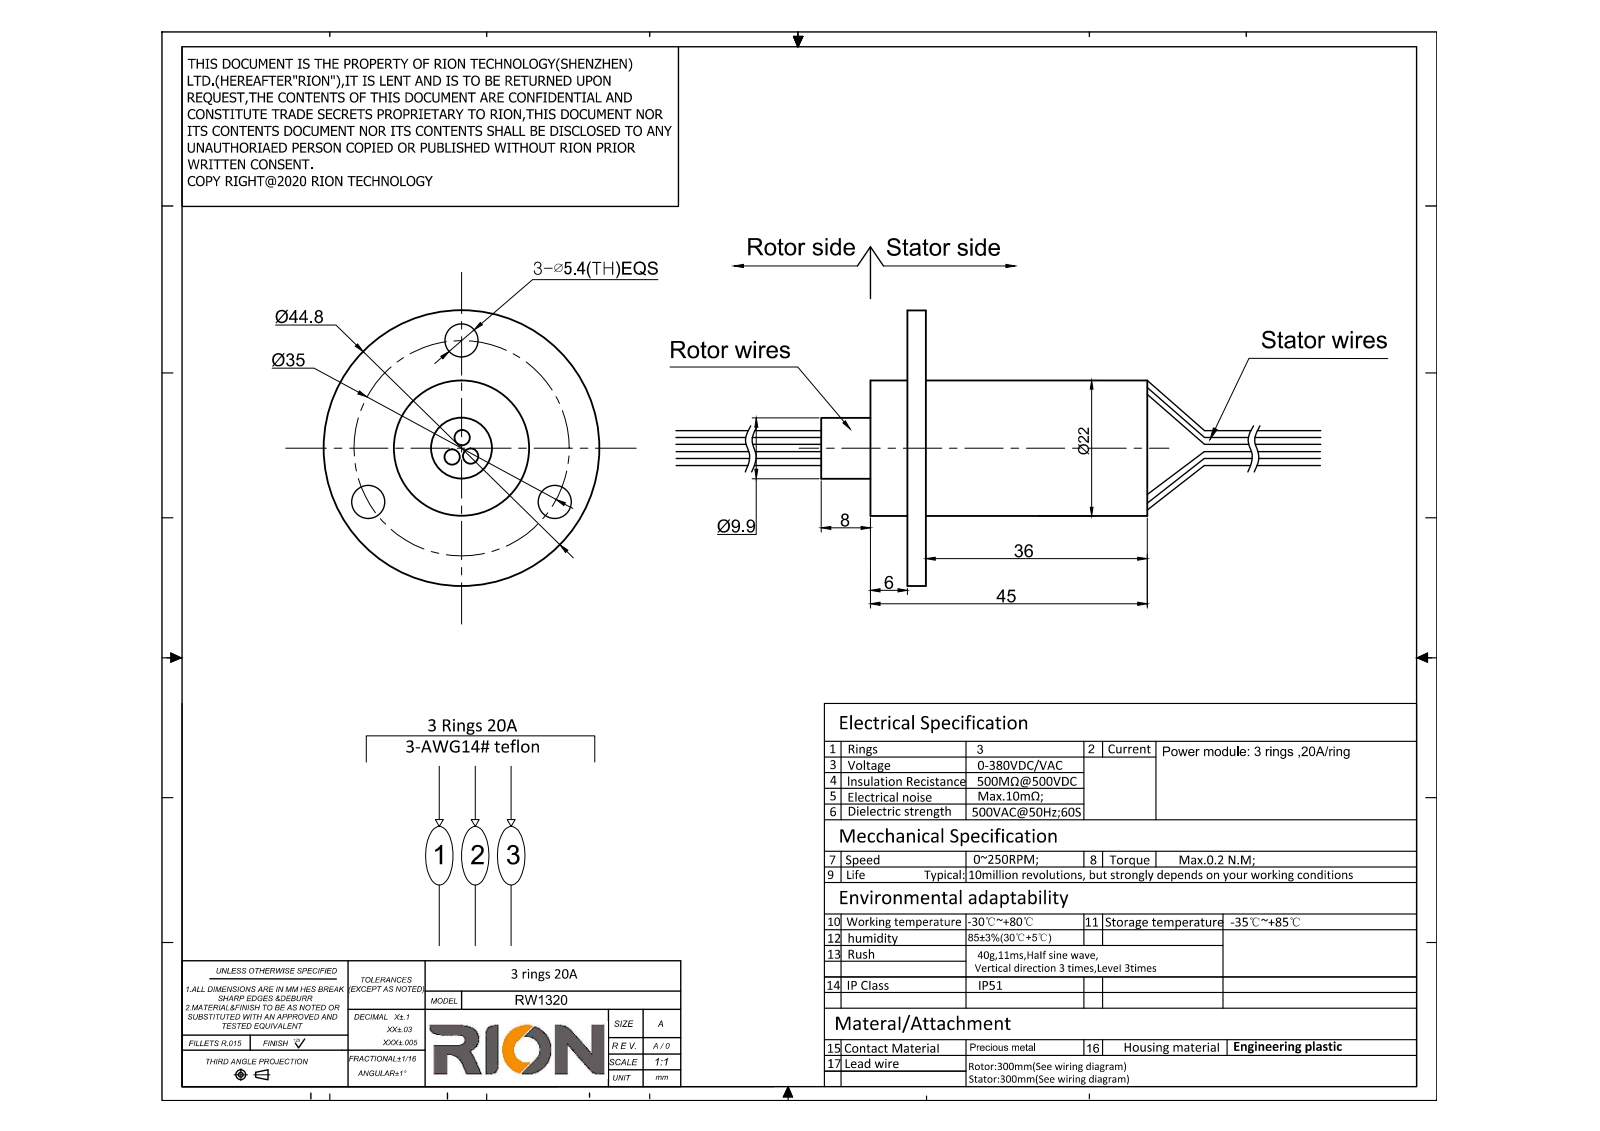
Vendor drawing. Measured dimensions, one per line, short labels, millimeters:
name: RW1215
written by: SolidWorks 2014 (CONFIG_CONTROL_DESIGN)
unit: mm
bodies: 1 solid, 61 faces (27 planar, 34 cylindrical, 0 other)
size: 92.7 × 44.8 × 44.8
volume: 21 674 mm³; area: 7 940 mm²
holes: 3× ⌀5.4, 1× ⌀6.62, 1× ⌀10.1, 1× ⌀20
bosses: 6× ⌀2.5, 1× ⌀44.8, 1× ⌀22, 1× ⌀19.9, 1× ⌀9.9
face distances: 3, 39, 36, 6, 9, 45, 8, 14, 17, 53
hole spacings: 17.5, 30.31, 30.32
